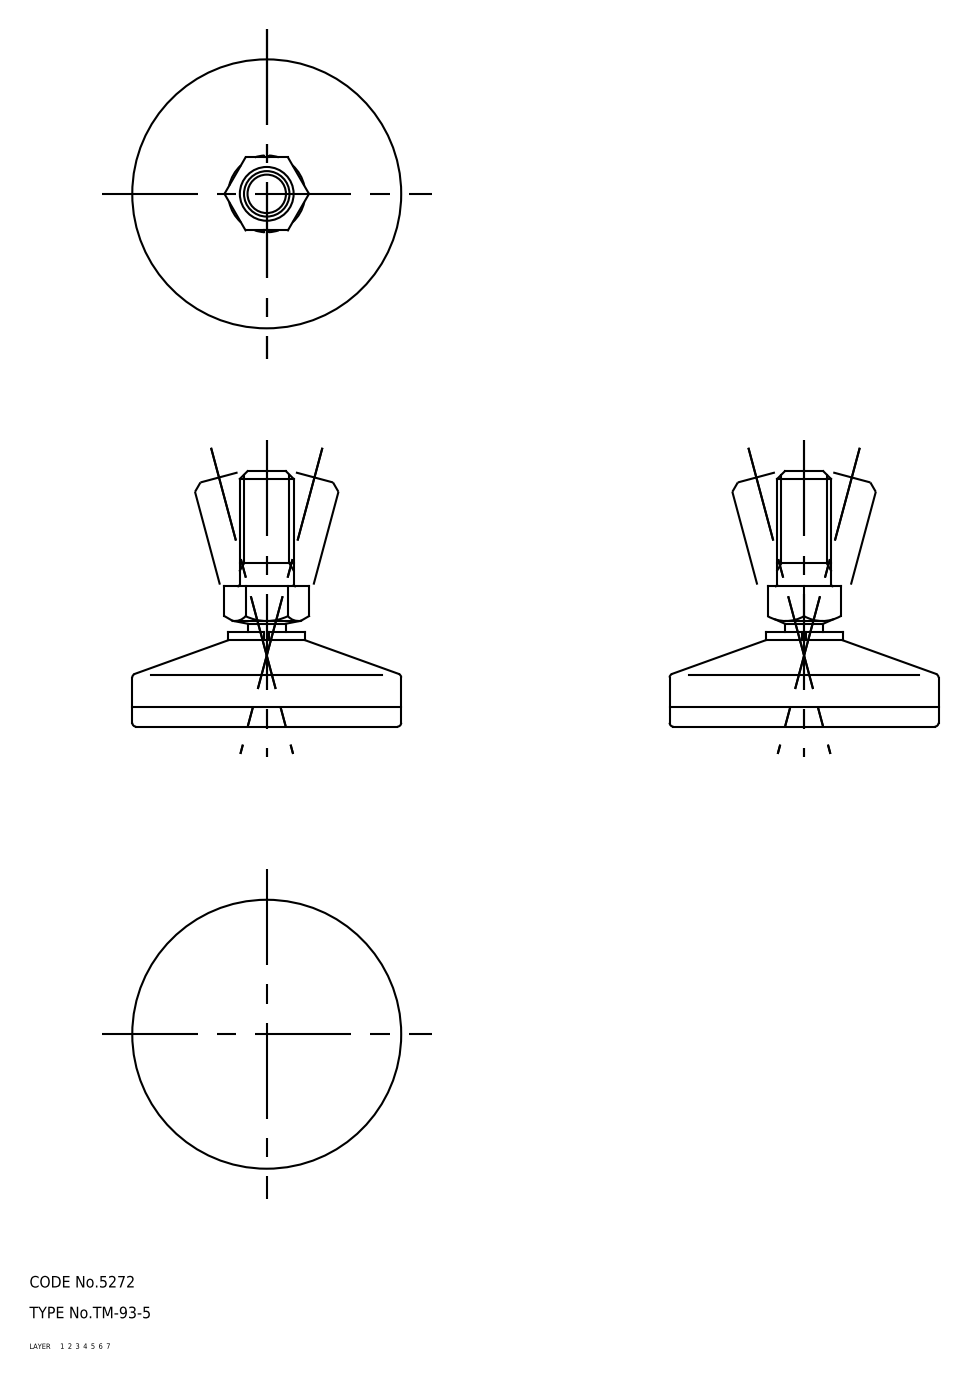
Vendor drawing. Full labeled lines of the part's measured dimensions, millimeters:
Part name (STEP PRODUCT): foot; cover; bolt; TM_93_5_7117_36
STEP written by: CADfix (AUTOMOTIVE_DESIGN)
Units: millimetres
Bodies: 3 solids, 78 faces (0 planar, 0 cylindrical, 78 other)
Overall size (bounding box): 70 × 70 × 66.5
Volume: 75 634 mm³ · Surface area: 26 453 mm²
